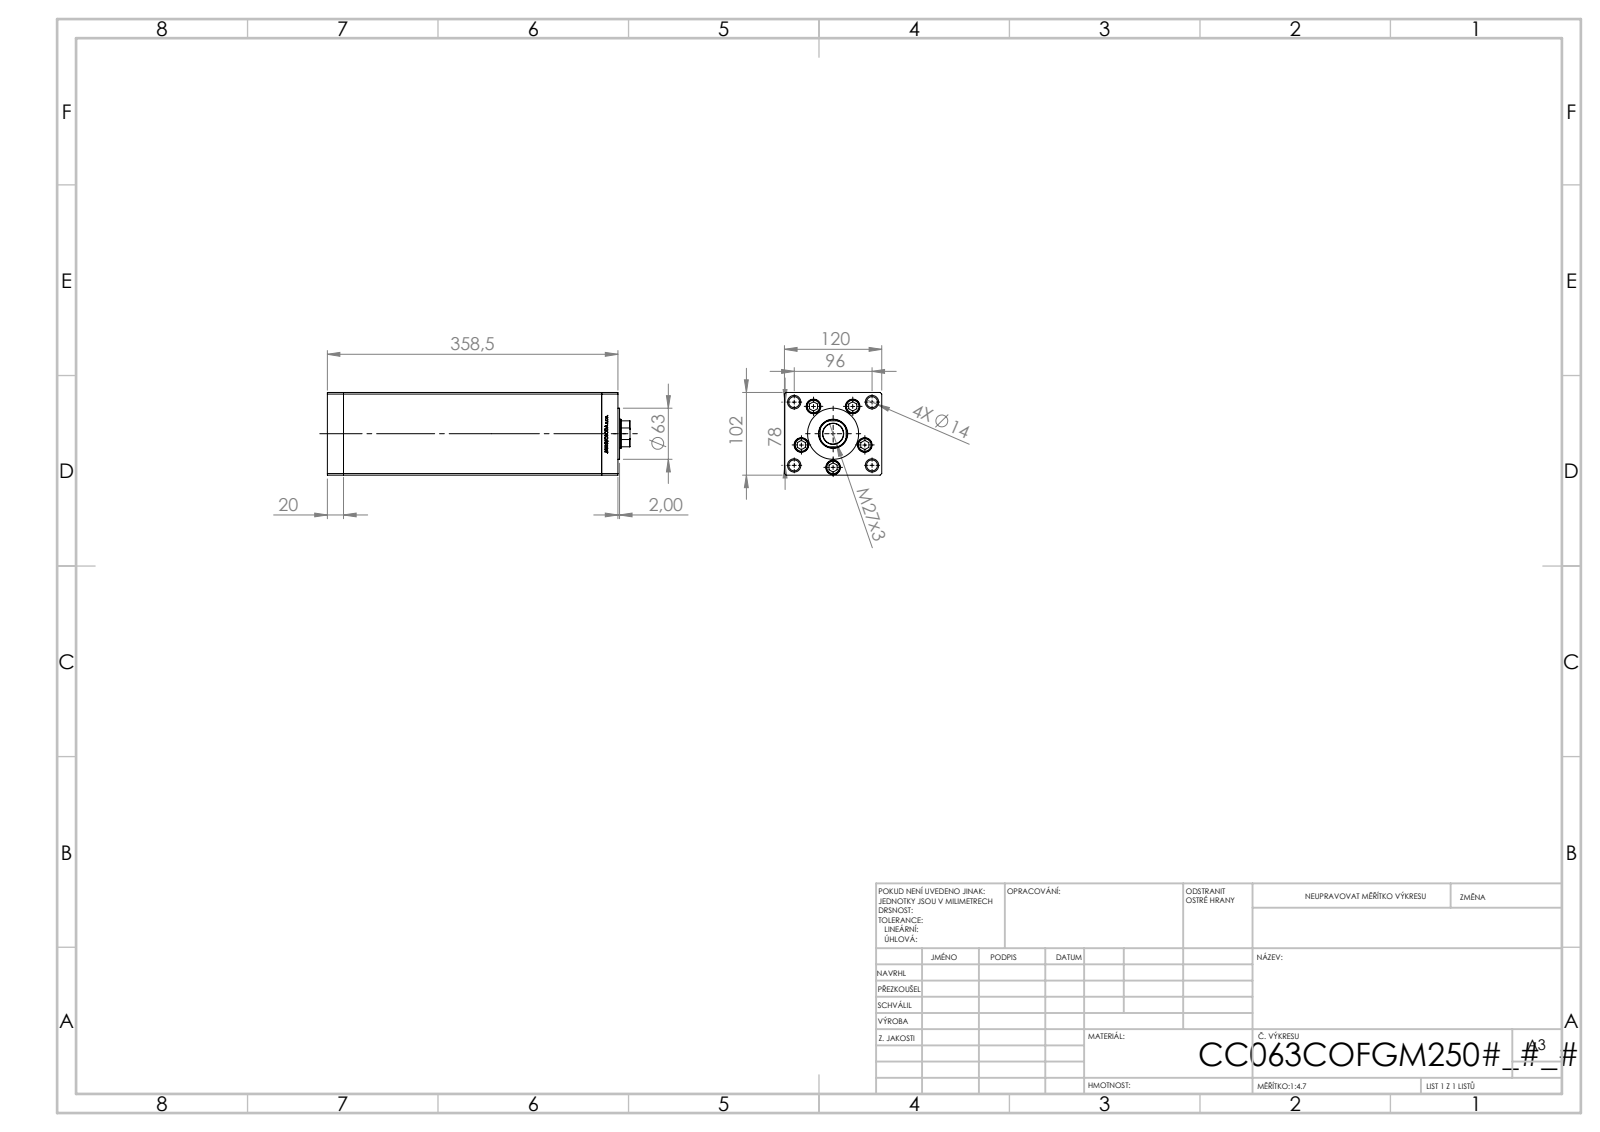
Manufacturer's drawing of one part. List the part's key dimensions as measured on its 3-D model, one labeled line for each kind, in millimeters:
Part name (STEP PRODUCT): V220C_VC_C; V220C BACK_C; V220C_C MIDDLE; V220C FRONT (+1 more)
STEP written by: SolidWorks 2019 (CONFIG_CONTROL_DESIGN)
Units: millimetres
Bodies: 13 solids, 1165 faces (542 planar, 161 cylindrical, 462 other)
Overall size (bounding box): 373.5 × 120 × 102
Volume: 3 632 000 mm³ · Surface area: 414 640 mm²
Round holes (diameter × count): ⌀13.5 ×9, ⌀18 ×5, ⌀12 ×4, ⌀16.5 ×4, ⌀17 ×1, ⌀25.5 ×1, ⌀36 ×1
Round bosses / shafts (diameter × count): ⌀8 ×5, ⌀17 ×4, ⌀63 ×1
Partial cylindrical surfaces — rounded edges, fillets, slot ends (radius × count): R0.93 ×2, R17.5 ×1
Main face-to-face distances: 120, 102, 20, 318.5, 338.5, 34.25, 358.5, 324.25, 304.25, 14.25
Hole centre spacings: 41.5, 61.85, 24.39, 26.69, 47.92, 48.07, 49.84, 53.57
